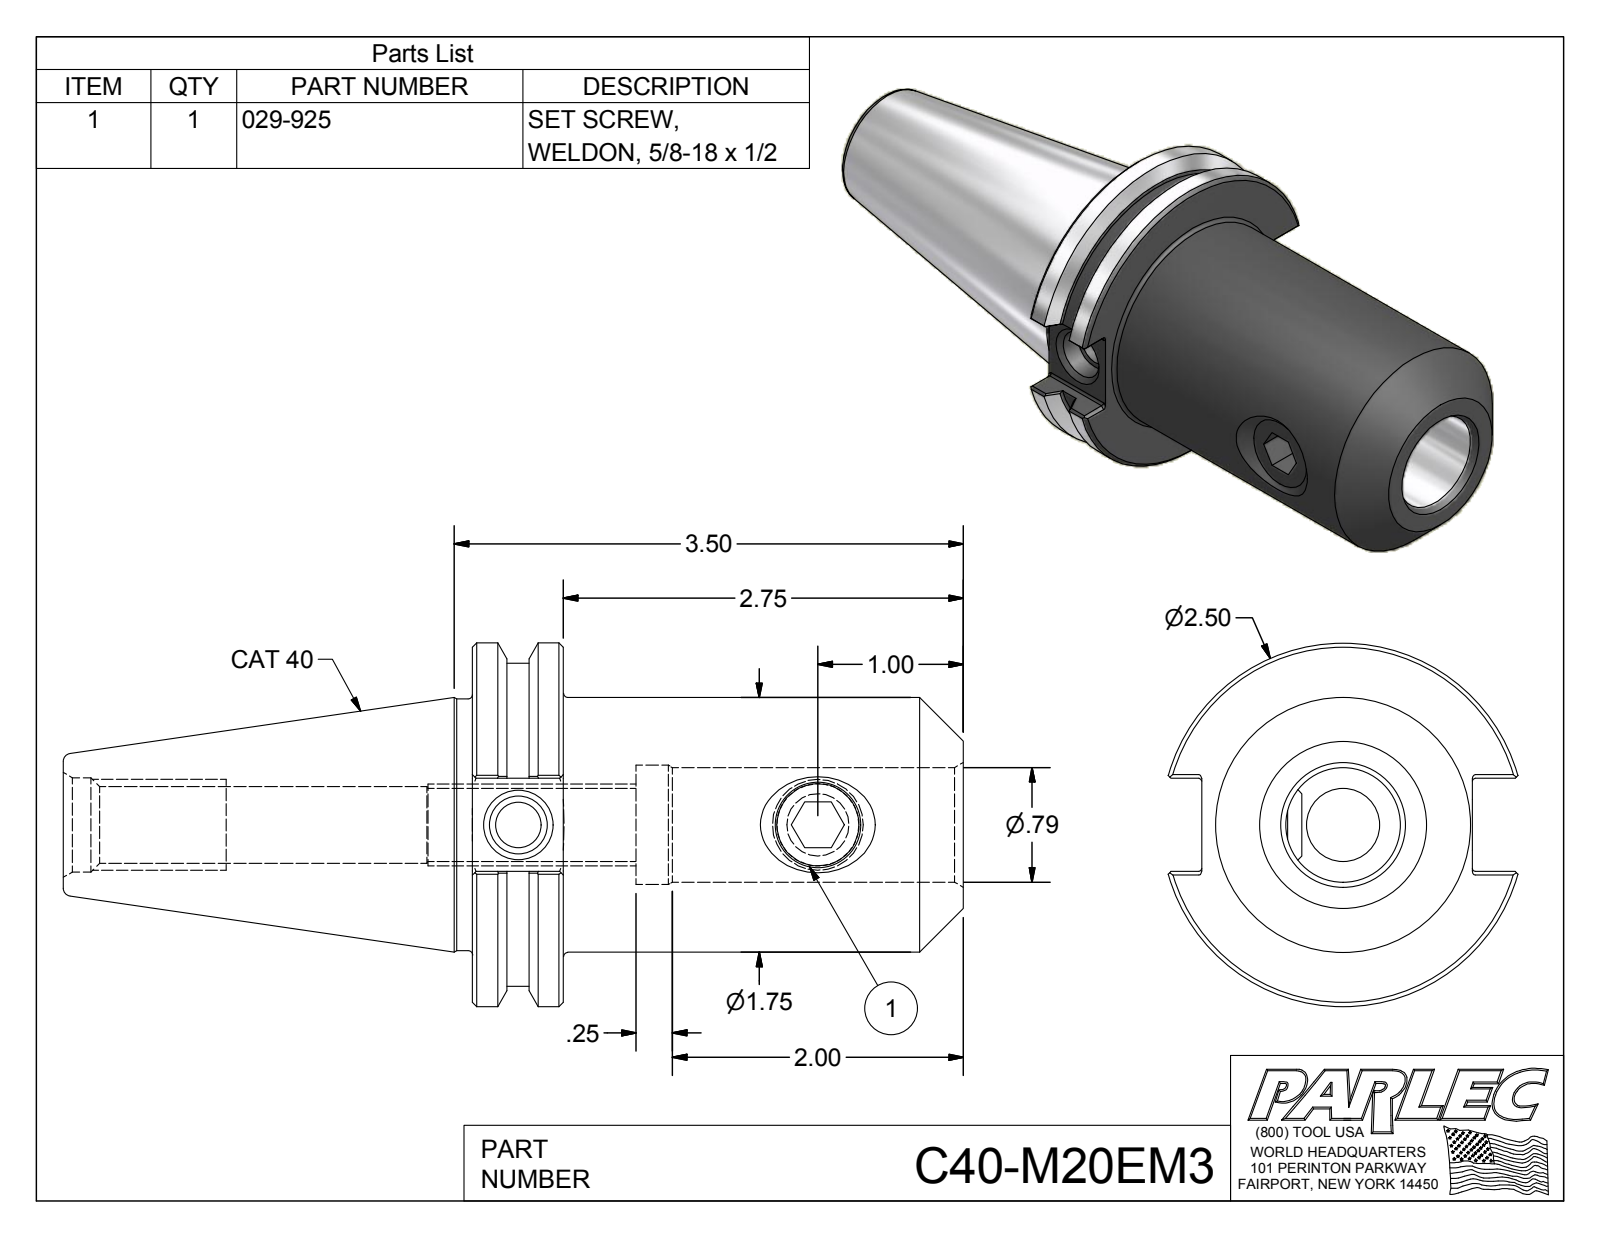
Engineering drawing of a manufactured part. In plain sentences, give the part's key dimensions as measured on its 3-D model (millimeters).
The part is named "C40-M20EM3; 029-925". Its 3-D file was written by "Autodesk Inventor 2012 (AUTOMOTIVE_DESIGN)". It is 2 solids with 102 faces: 41 planar, 29 cylindrical and 32 other. Overall it measures 157.1 by 63.5 by 61.1 millimeters. Its volume is 185 300 cubic millimeters and its surface area 34 680 square millimeters. Round holes: 1 of diameter 8, 1 of diameter 10.1, 1 of diameter 12.8, 1 of diameter 13.4, 1 of diameter 14.4, 1 of diameter 16.5, 1 of diameter 20, 1 of diameter 20.8. Round bosses or shafts: 1 of diameter 63.5, 1 of diameter 56.4, 1 of diameter 44.5, 1 of diameter 43.9, 1 of diameter 15.9. Partial cylindrical surfaces (rounded edges, fillets, slot ends): 12 of radius 0.5. The main face-to-face distances are 15.9, 12.7, 85.7, 69.9, 28.6, 57.2, 16.3, 8, 47.2, 71.4. The hole center spacings are 52.3.
